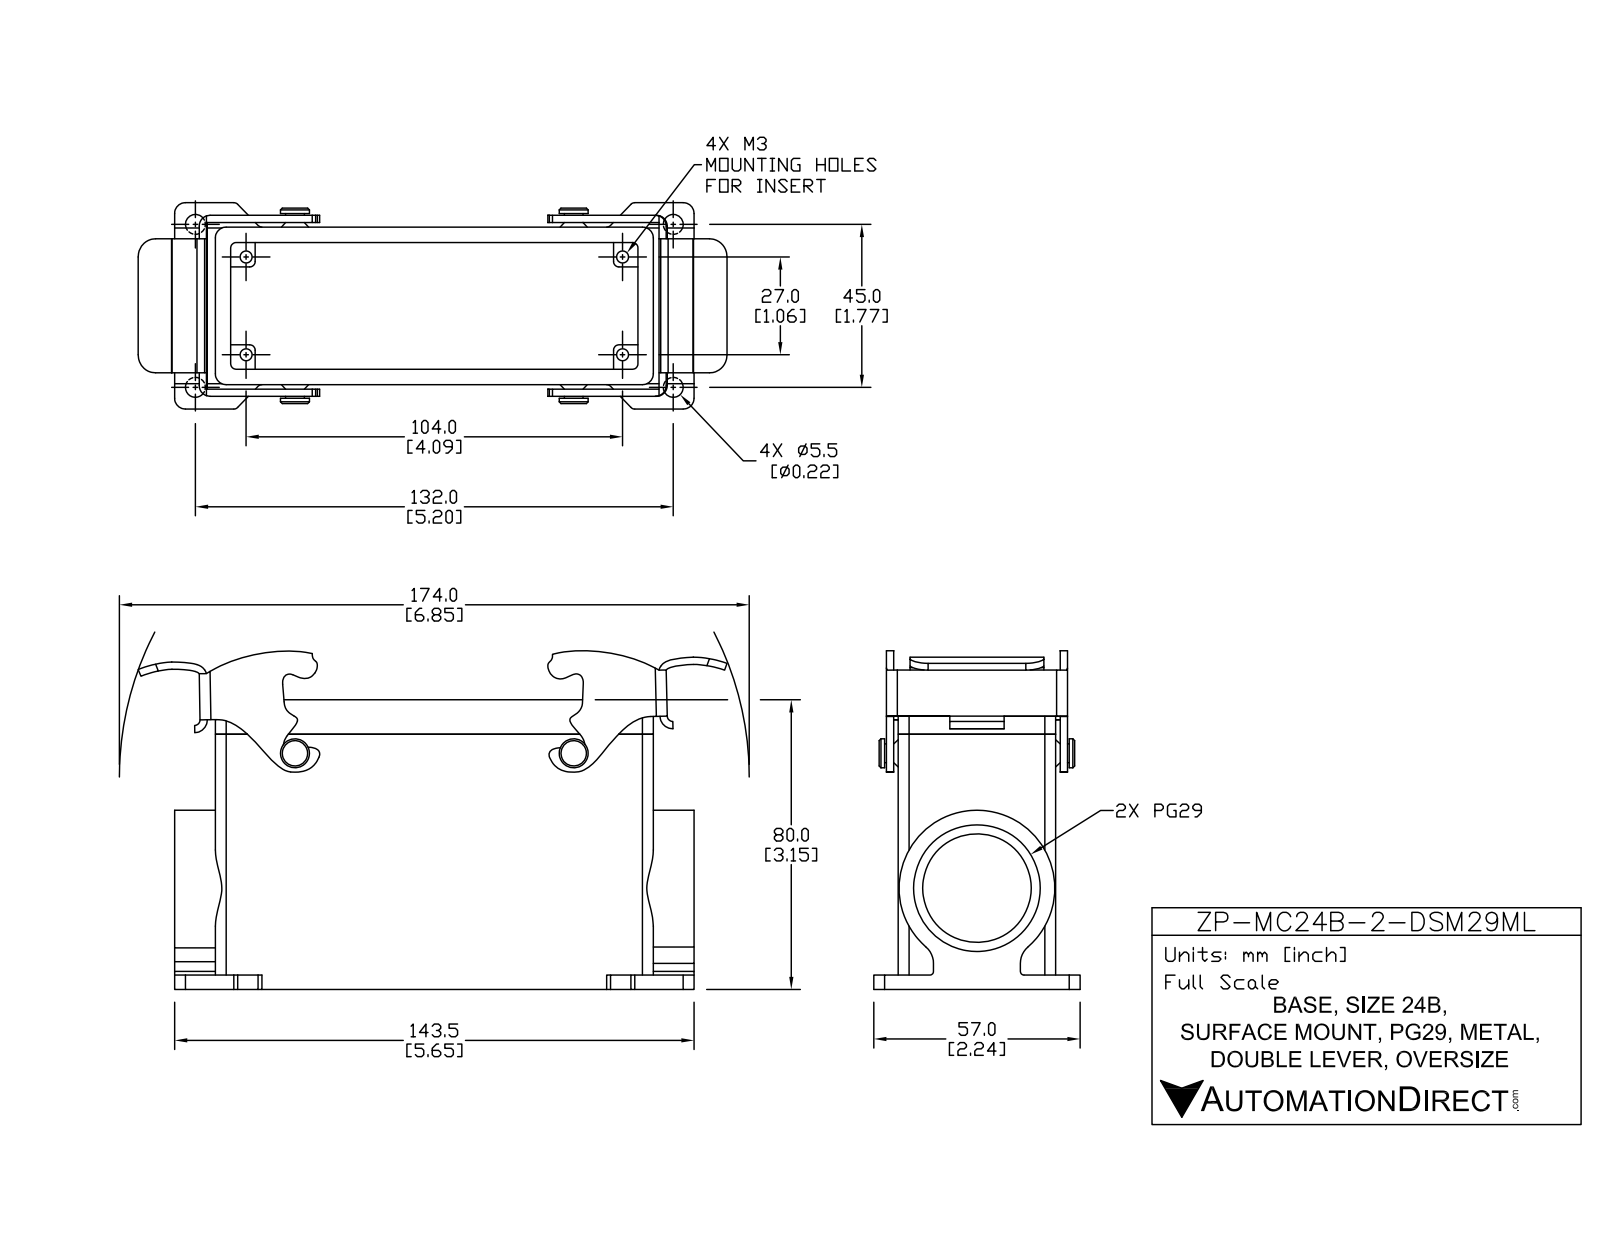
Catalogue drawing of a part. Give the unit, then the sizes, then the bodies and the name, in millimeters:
Units: millimetres
Overall size (bounding box): 172.9 × 90.67 × 57
Round holes (diameter × count): ⌀3.3 ×4, ⌀5.5 ×4, ⌀30 ×1, ⌀35 ×1
Round bosses / shafts (diameter × count): ⌀8 ×2, ⌀5.17 ×2
Partial cylindrical surfaces — rounded edges, fillets, slot ends (radius × count): R0.5 ×26, R1.5 ×16, R3 ×10, R1 ×6, R2 ×6, R4 ×6, R5 ×4, R10 ×4
Main face-to-face distances: 4.25, 39.25, 43.5, 35, 2.5, 1.15, 70.5, 68, 5.5, 116.75
Hole centre spacings: 16.64, 38.63, 118.34, 123.37, 27, 45, 104, 107.45
Volume: 142 861 mm³ · Surface area: 80 152 mm²
Bodies: 4 solids, 329 faces (135 planar, 186 cylindrical, 8 other)
Part name (STEP PRODUCT): ZP-MC24B-2-DSM29ML
STEP written by: SolidWorks 2011 (AUTOMOTIVE_DESIGN)
